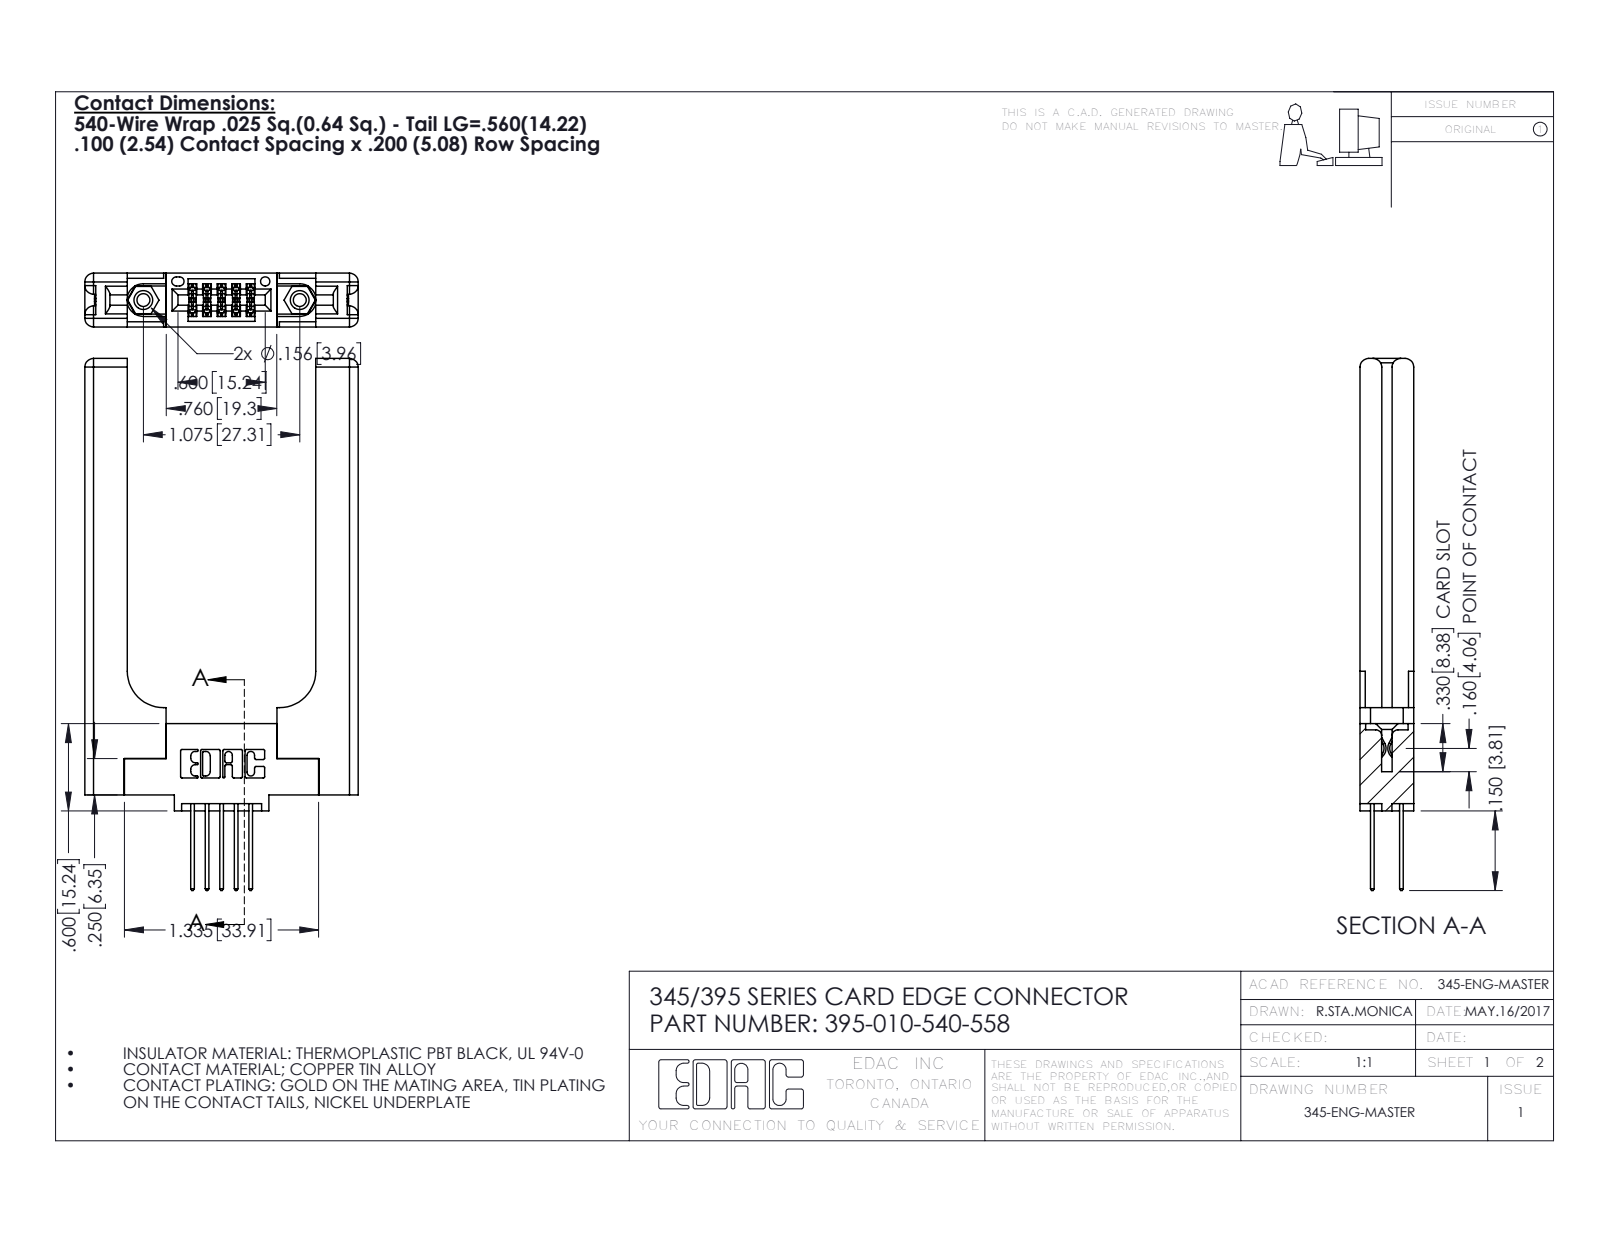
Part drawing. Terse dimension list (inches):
name: 345-250-001_345-250-001-102; 345-292-001_345-293-140; 345-220-058_345-220-058; 395-010-540-558 (+1 more)
written by: SolidWorks 2016 (CONFIG_CONTROL_DESIGN)
unit: in
bodies: 15 solids, 886 faces (562 planar, 264 cylindrical, 60 other)
size: 3.657 × 1.879 × 0.37
volume: 0.777 in³; area: 16.9 in²
holes: 2× ⌀0.089, 2× ⌀0.125, 2× ⌀0.156, 1× ⌀0.064
bosses: 2× ⌀0.155
rounds: 22× R0.01, 16× R0.06, 15× R0.006, 10× R0.01, 6× R0.007, 6× R0.031, 3× R0.026, 2× R0.014
face distances: 0.37, 0.15, 0.22, 0.072, 0.148, 0.077, 0.298, 1.296, 0.071, 0.292
hole spacings: 0.27, 0.847, 1.075
